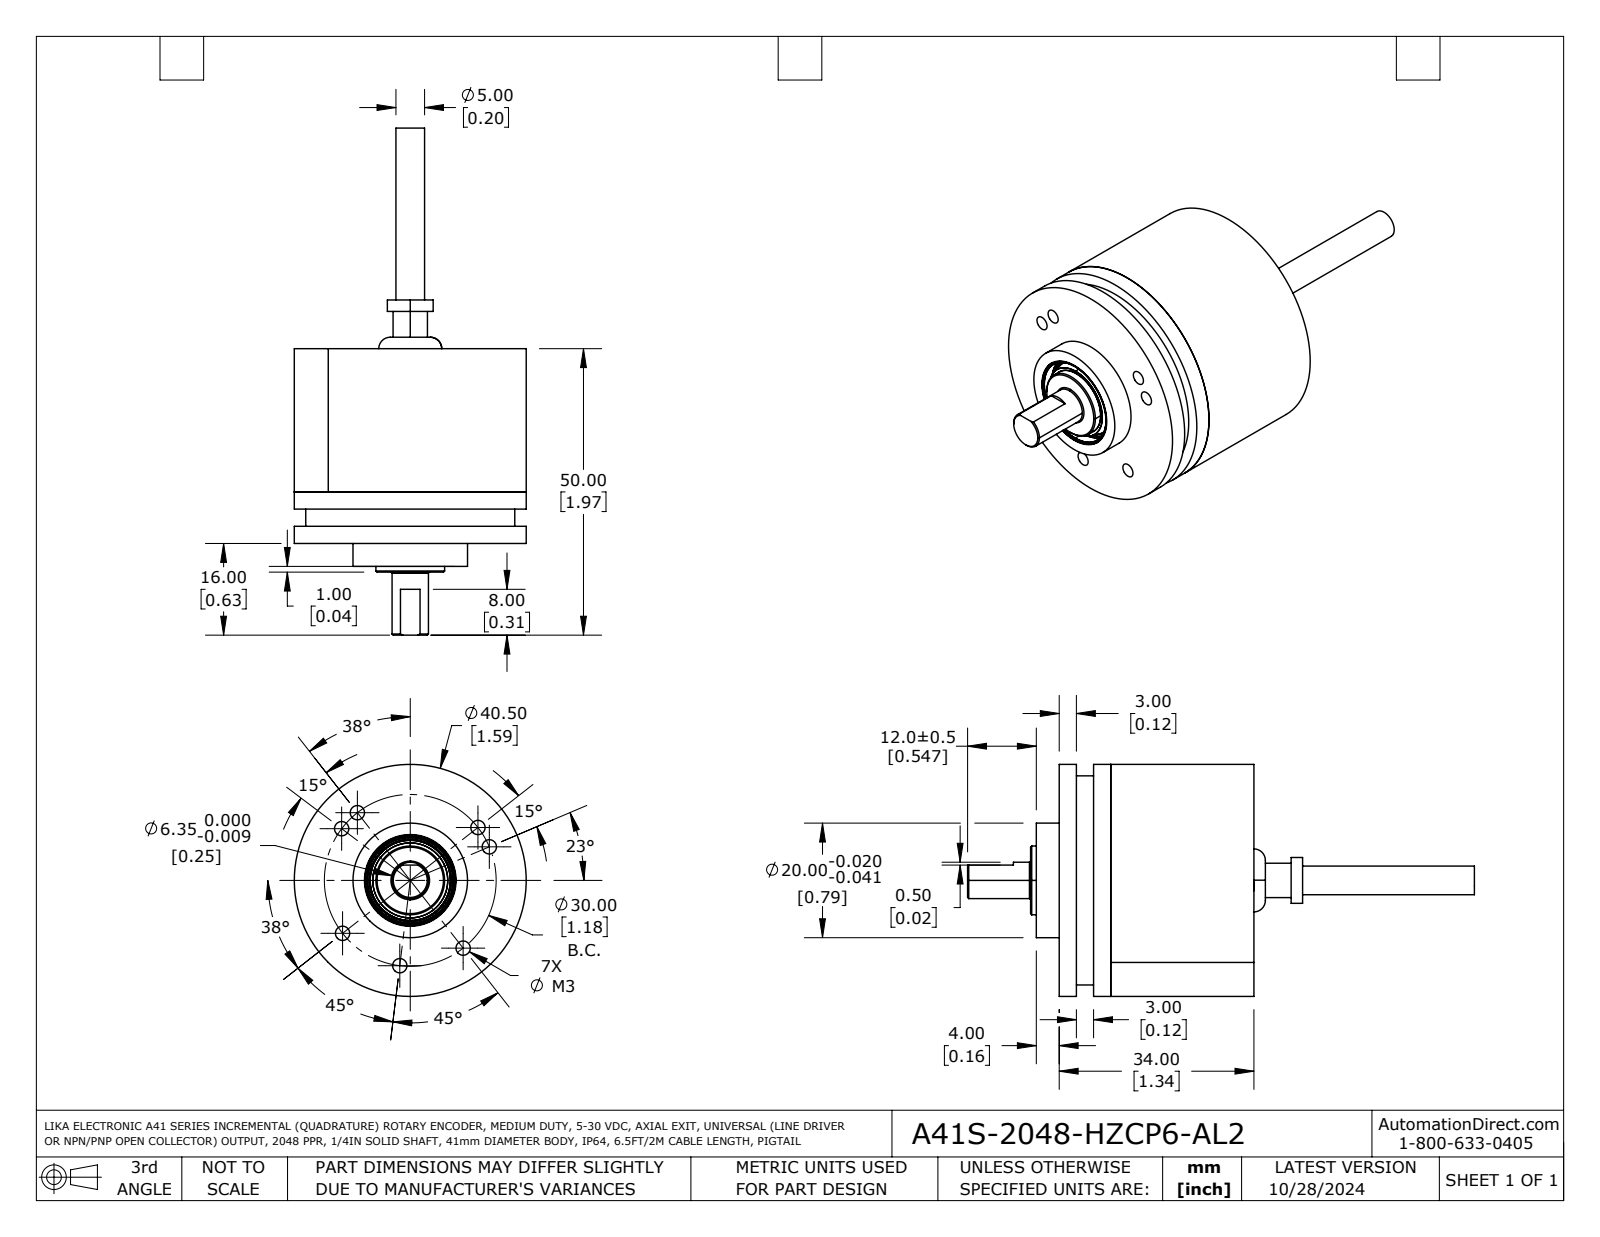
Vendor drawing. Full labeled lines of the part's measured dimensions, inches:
Part name (STEP PRODUCT): A41S-2048-HZCP6-AL2
STEP written by: SolidWorks 2021 (AUTOMOTIVE_DESIGN)
Units: inches
Bodies: 11 solids, 422 faces (76 planar, 145 cylindrical, 201 other)
Overall size (bounding box): 3.484 × 1.594 × 1.594
Volume: 1.175 in³ · Surface area: 28.29 in²
Round holes (diameter × count): ⌀0.063 ×7, ⌀0.098 ×7, ⌀0.157 ×3, ⌀0.087 ×2, ⌀0.169 ×1, ⌀0.295 ×1, ⌀0.512 ×1, ⌀0.602 ×1, ⌀0.612 ×1, ⌀0.63 ×1, ⌀1.516 ×1
Round bosses / shafts (diameter × count): ⌀0.079 ×2, ⌀1.594 ×1, ⌀1.496 ×1, ⌀1.457 ×1, ⌀1.437 ×1, ⌀0.787 ×1, ⌀0.472 ×1, ⌀0.315 ×1
Partial cylindrical surfaces — rounded edges, fillets, slot ends (radius × count): R0.039 ×14, R0.007 ×6, R0.008 ×2
Main face-to-face distances: 0.118, 1.339, 0.433, 0.906, 1.22, 0.079, 0.866, 0.984, 0.787, 0.039
Hole centre spacings: 0.591, 0.669, 0.835, 0.11, 0.118, 0.837, 0.945, 1.257
